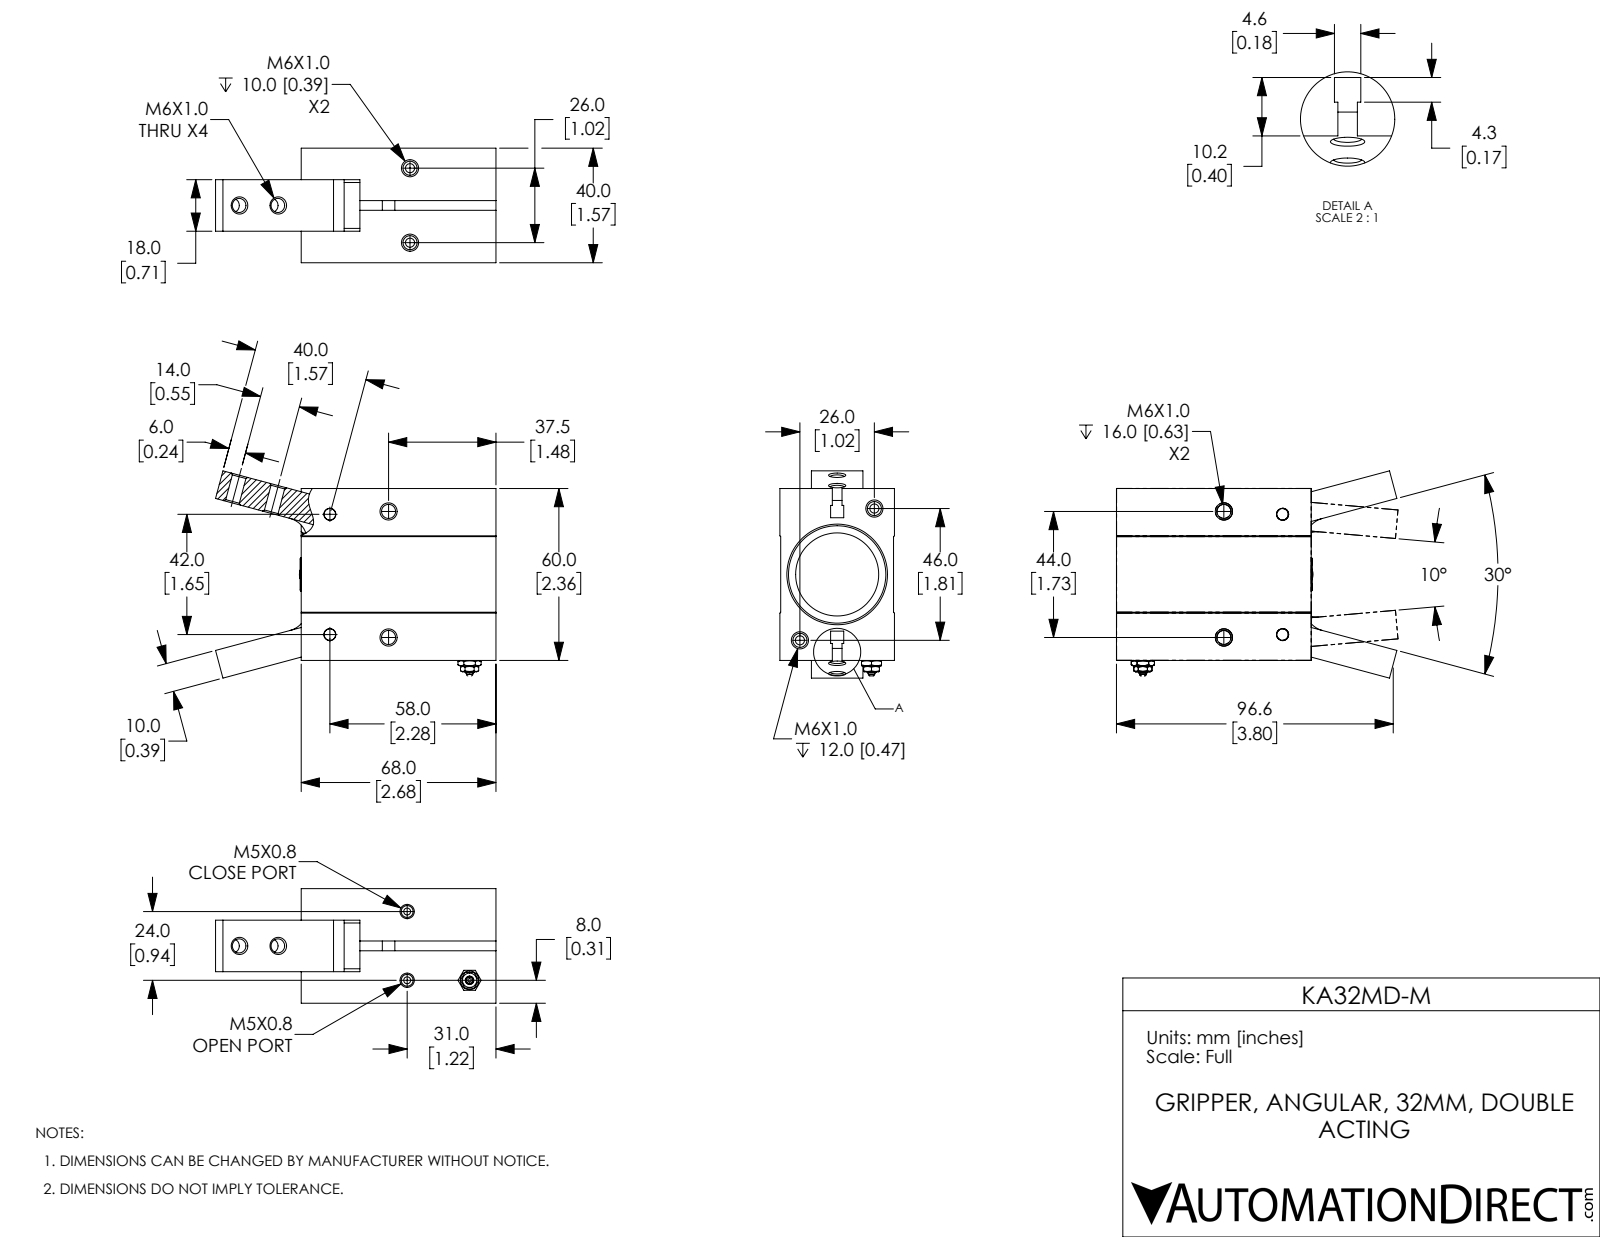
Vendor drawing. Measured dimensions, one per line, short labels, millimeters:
name: KA32MD-M; KA32MD-M-4; KA32MD-M-3; KA32MD-M-2 (+1 more)
written by: SolidWorks 2017 (AUTOMOTIVE_DESIGN)
unit: mm
bodies: 4 solids, 277 faces (111 planar, 88 cylindrical, 78 other)
size: 97.93 × 72.36 × 40
volume: 133 554 mm³; area: 43 456 mm²
holes: 6× ⌀4.92, 4× ⌀4.92, 2× ⌀4, 2× ⌀4.13, 2× ⌀6.2, 1× ⌀3, 1× ⌀16, 1× ⌀29, 1× ⌀32, 1× ⌀34, 1× ⌀35
bosses: 1× ⌀31.5, 1× ⌀15, 1× ⌀10, 1× ⌀3, 1× ⌀2.2
rounds: 2× R5, 2× R8
face distances: 10.7, 39.7, 11, 29, 28.7, 18, 40, 60, 39.4, 10
hole spacings: 1.41, 14, 20.52, 21.9, 25.02, 26.42, 34.6, 47.64
